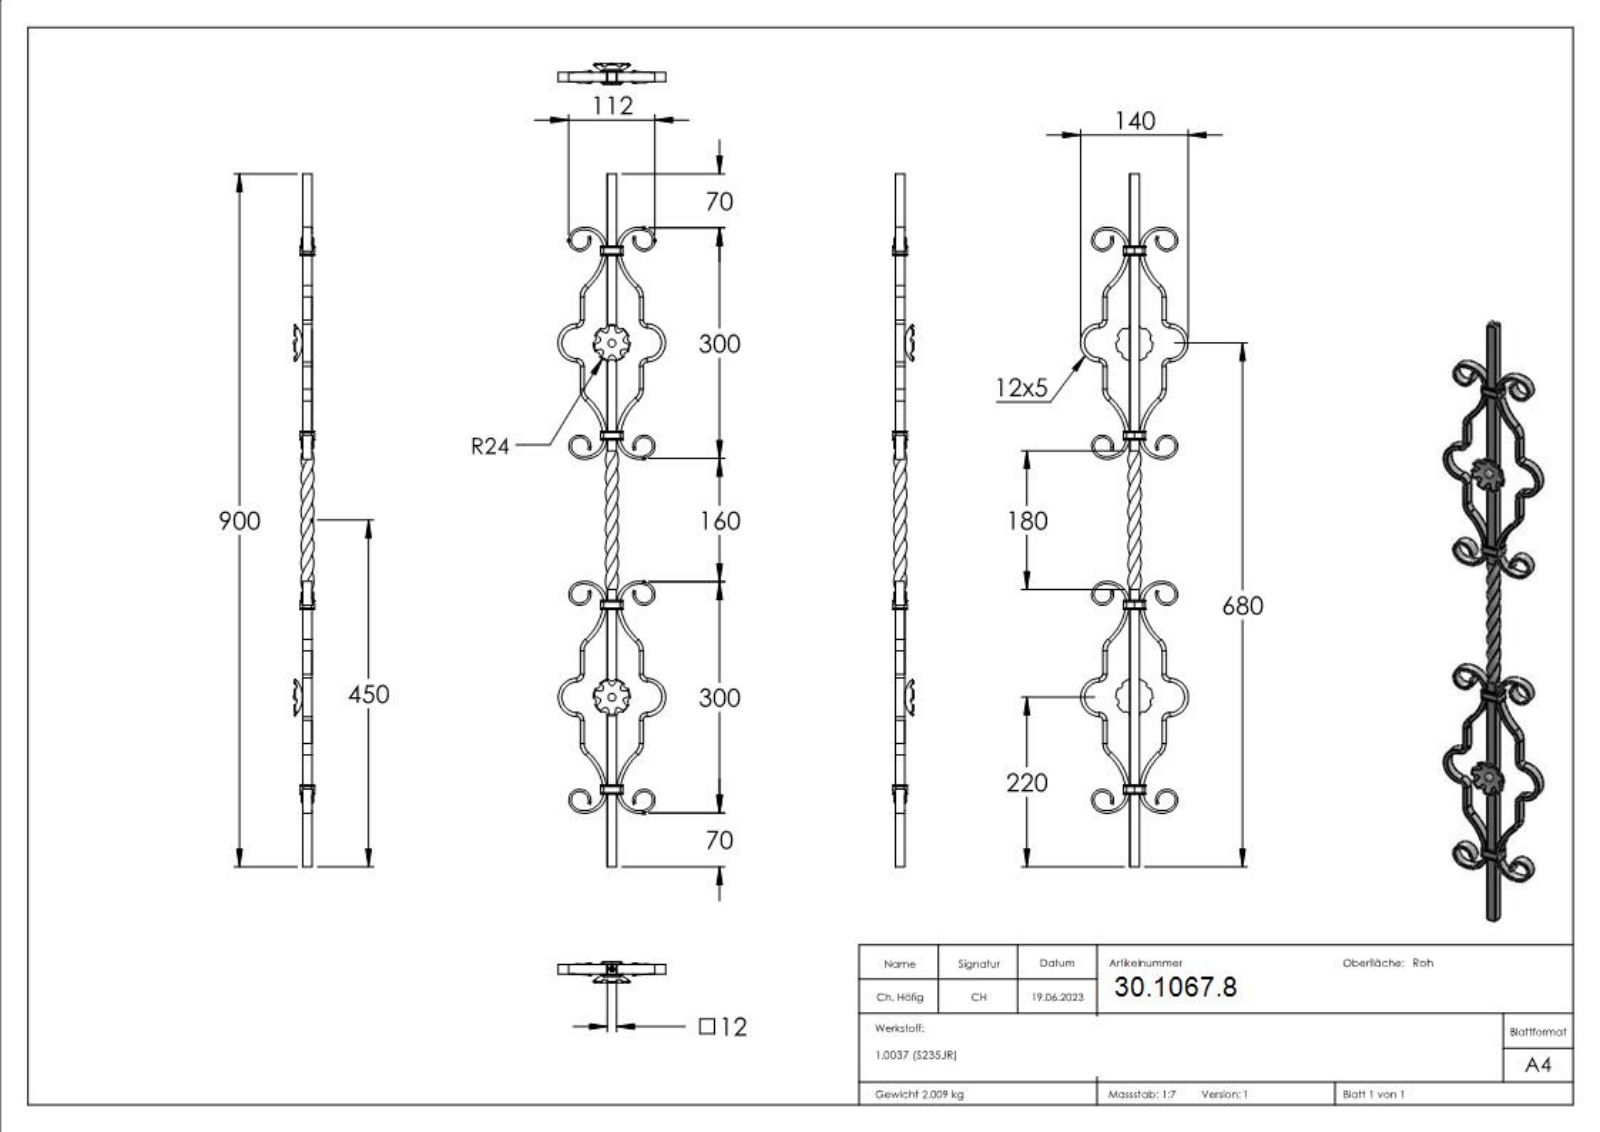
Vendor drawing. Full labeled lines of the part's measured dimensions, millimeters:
Part name (STEP PRODUCT): 1224
STEP written by: SolidWorks 2018 (CONFIG_CONTROL_DESIGN)
Units: millimetres
Bodies: 5 solids, 1033 faces (437 planar, 300 cylindrical, 296 other)
Overall size (bounding box): 900 × 140 × 27.5
Volume: 257 571 mm³ · Surface area: 130 567 mm²
Round bosses / shafts (diameter × count): ⌀12 ×2
Partial cylindrical surfaces — rounded edges, fillets, slot ends (radius × count): R0.5 ×88, R0.2 ×32, R10.62 ×16, R6.5 ×14, R20 ×12, R5 ×8, R10 ×8, R15 ×8
Main face-to-face distances: 12, 5, 35, 42, 47, 77, 30, 12.5, 0.5, 82
